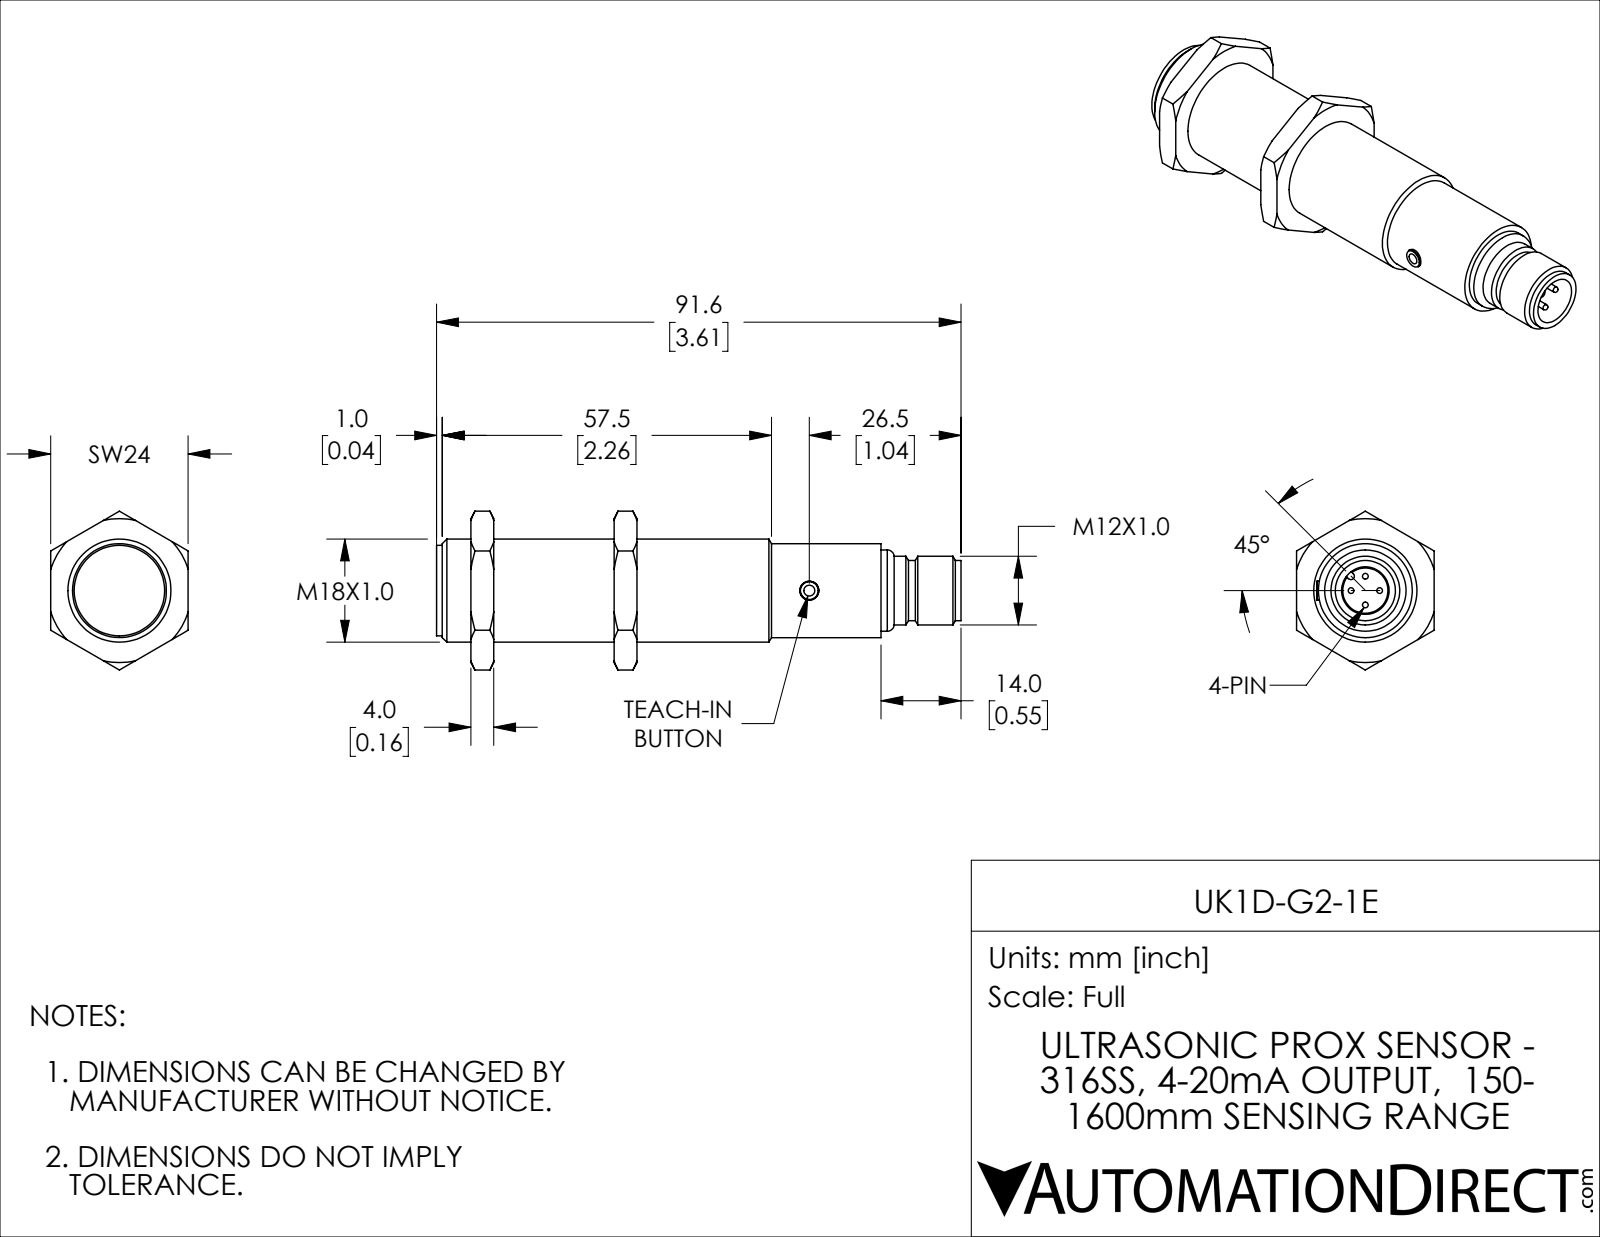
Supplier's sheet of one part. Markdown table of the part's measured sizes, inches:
| quantity | value |
| --- | --- |
| part name | UK1D-G2-1E |
| STEP written by | SolidWorks 2018 (AUTOMOTIVE_DESIGN) |
| units | inches |
| bodies | 4 solids, 113 faces (27 planar, 35 cylindrical, 51 other) |
| overall size | 3.606 × 1.091 × 0.945 |
| volume | 1.338 in³ |
| surface area | 11.97 in² |
| round holes (diameter × count) | 0.13 × 1, 0.327 × 1, 0.709 × 1 |
| round bosses / shafts (diameter × count) | 0.039 × 4, 0.646 × 1, 0.622 × 1, 0.559 × 1, 0.472 × 1, 0.413 × 1 |
| partial cylindrical surfaces (radius × count) | 0.024 × 1 |
| main face-to-face distances | 0.984, 0.157, 0.945, 1.142, 0.827, 0.236, 0.394, 1.22, 1.378, 3.055 |
